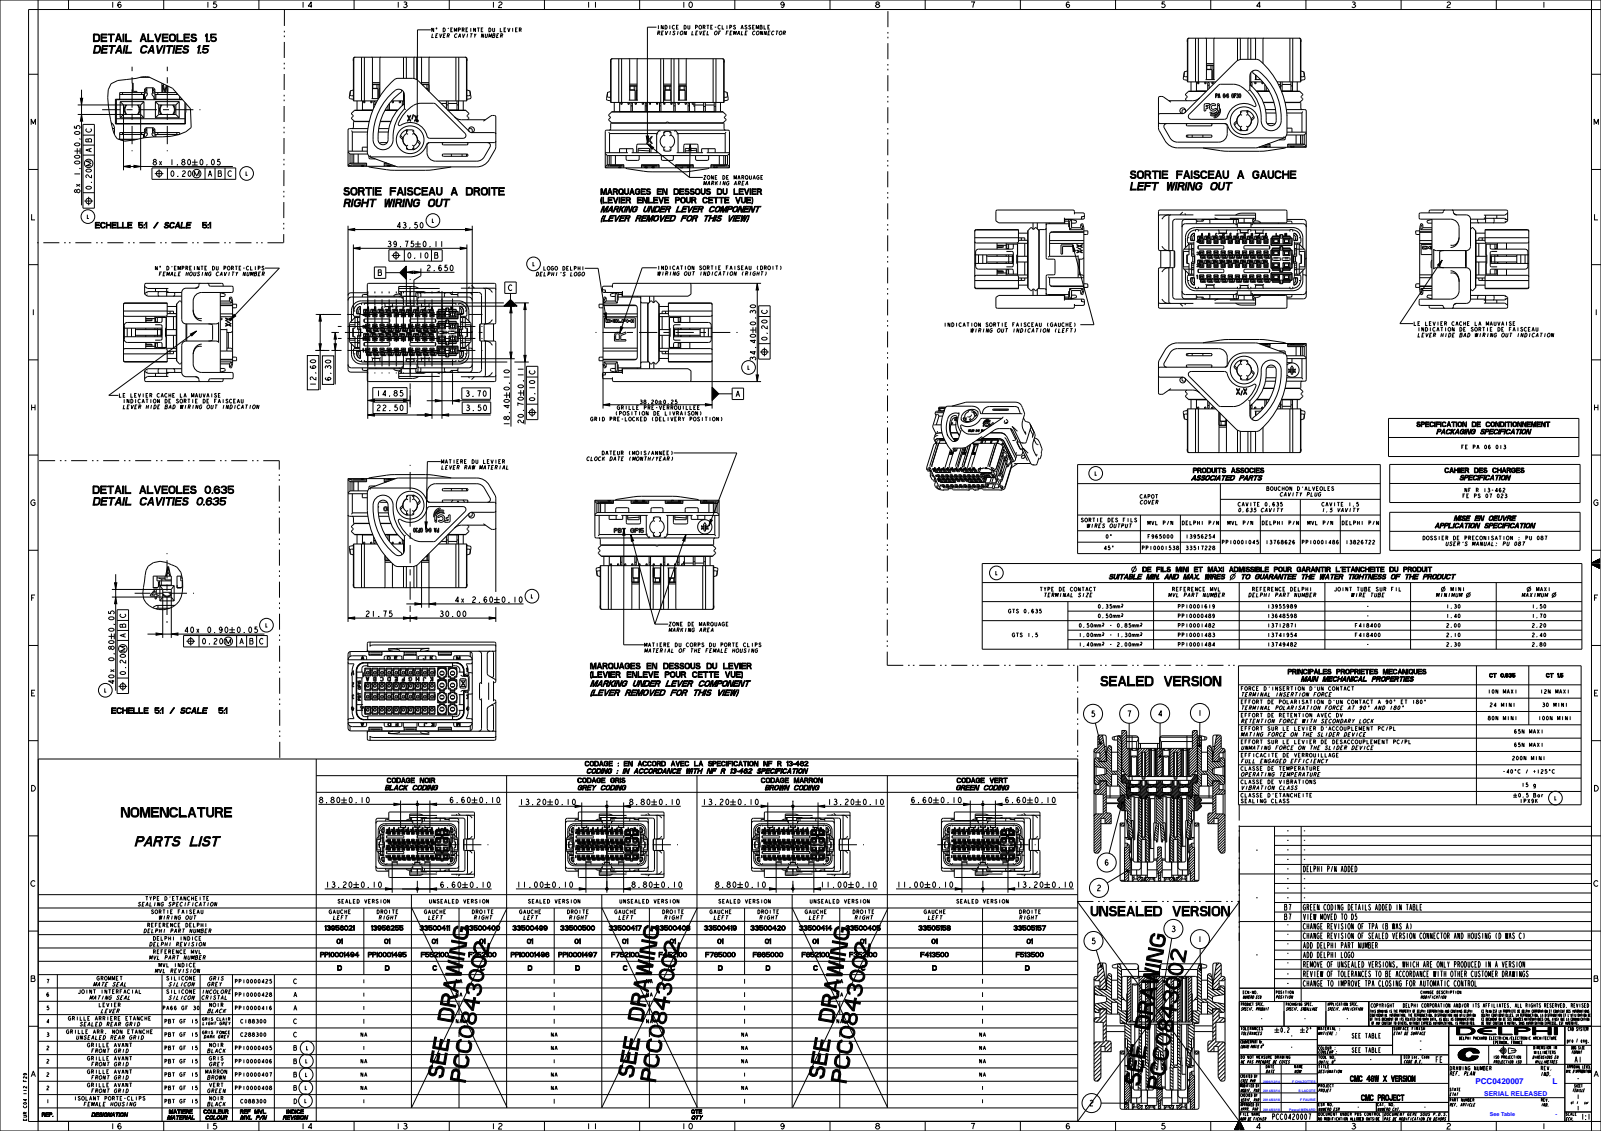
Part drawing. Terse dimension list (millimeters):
written by: SIEMENS PLM Software NX 9.0 (AP203_CONFIGURATION_CONTROLLED_3D_DESIGN_OF_MECHANICAL_PARTS_AND_ASSEMBLIES_MIM_LF)
unit: mm
bodies: 1 solid, 2103 faces (1767 planar, 190 cylindrical, 146 other)
size: 51.75 × 36.6 × 34.4
volume: 31 722 mm³; area: 21 160 mm²
bosses: 1× ⌀5.05
rounds: 18× R1.5, 15× R1, 12× R2.7, 8× R0.15, 8× R0.2, 8× R0.3, 8× R2.8, 5× R0.2
face distances: 0.8, 1, 6.2, 1.1, 3, 27.2, 3.8, 20.1, 25, 23.9
